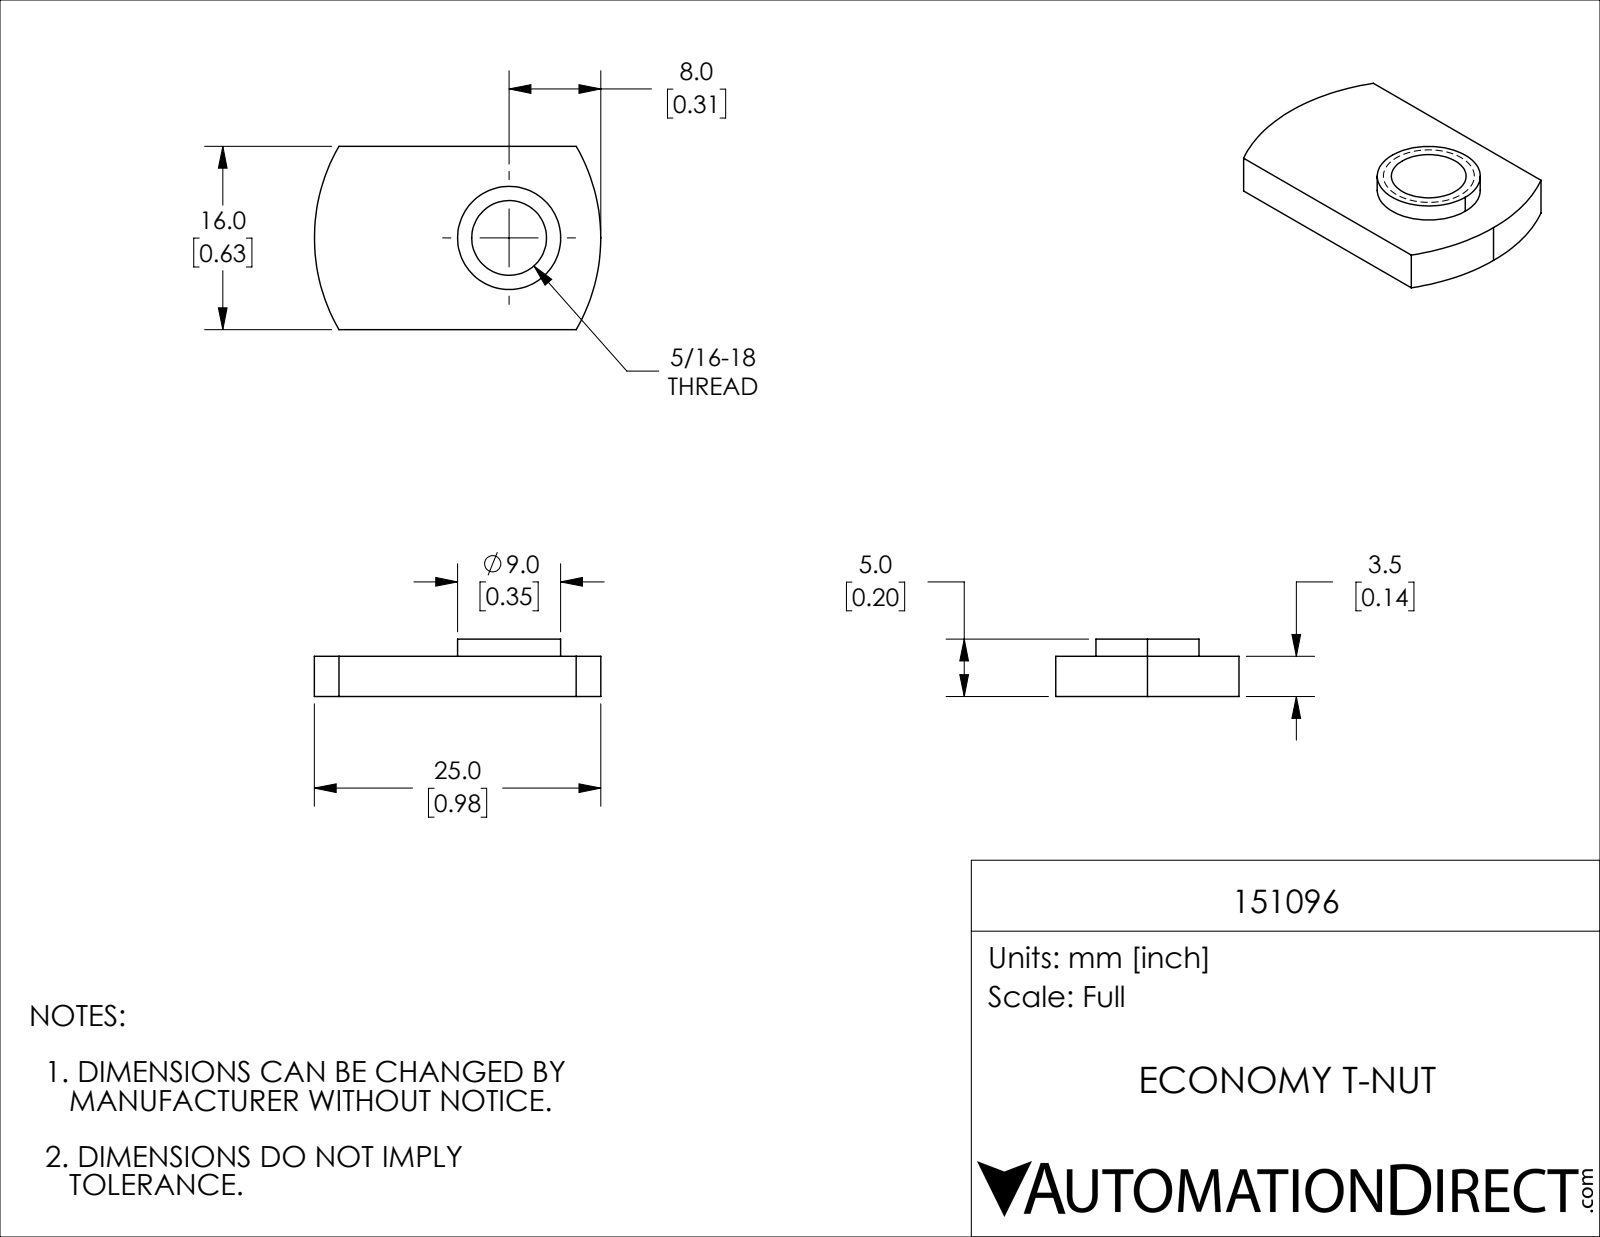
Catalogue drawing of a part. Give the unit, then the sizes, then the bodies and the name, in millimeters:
Units: millimetres
Overall size (bounding box): 25 × 16 × 5
Round holes (diameter × count): ⌀6.53 ×1
Round bosses / shafts (diameter × count): ⌀9 ×1
Partial cylindrical surfaces — rounded edges, fillets, slot ends (radius × count): R16 ×2
Main face-to-face distances: 3.5, 16, 5, 1.5
Volume: 1 250 mm³ · Surface area: 1 096 mm²
Bodies: 1 solid, 12 faces (5 planar, 7 cylindrical, 0 other)
Part name (STEP PRODUCT): 151096
STEP written by: SolidWorks 2021 (CONFIG_CONTROL_DESIGN)
